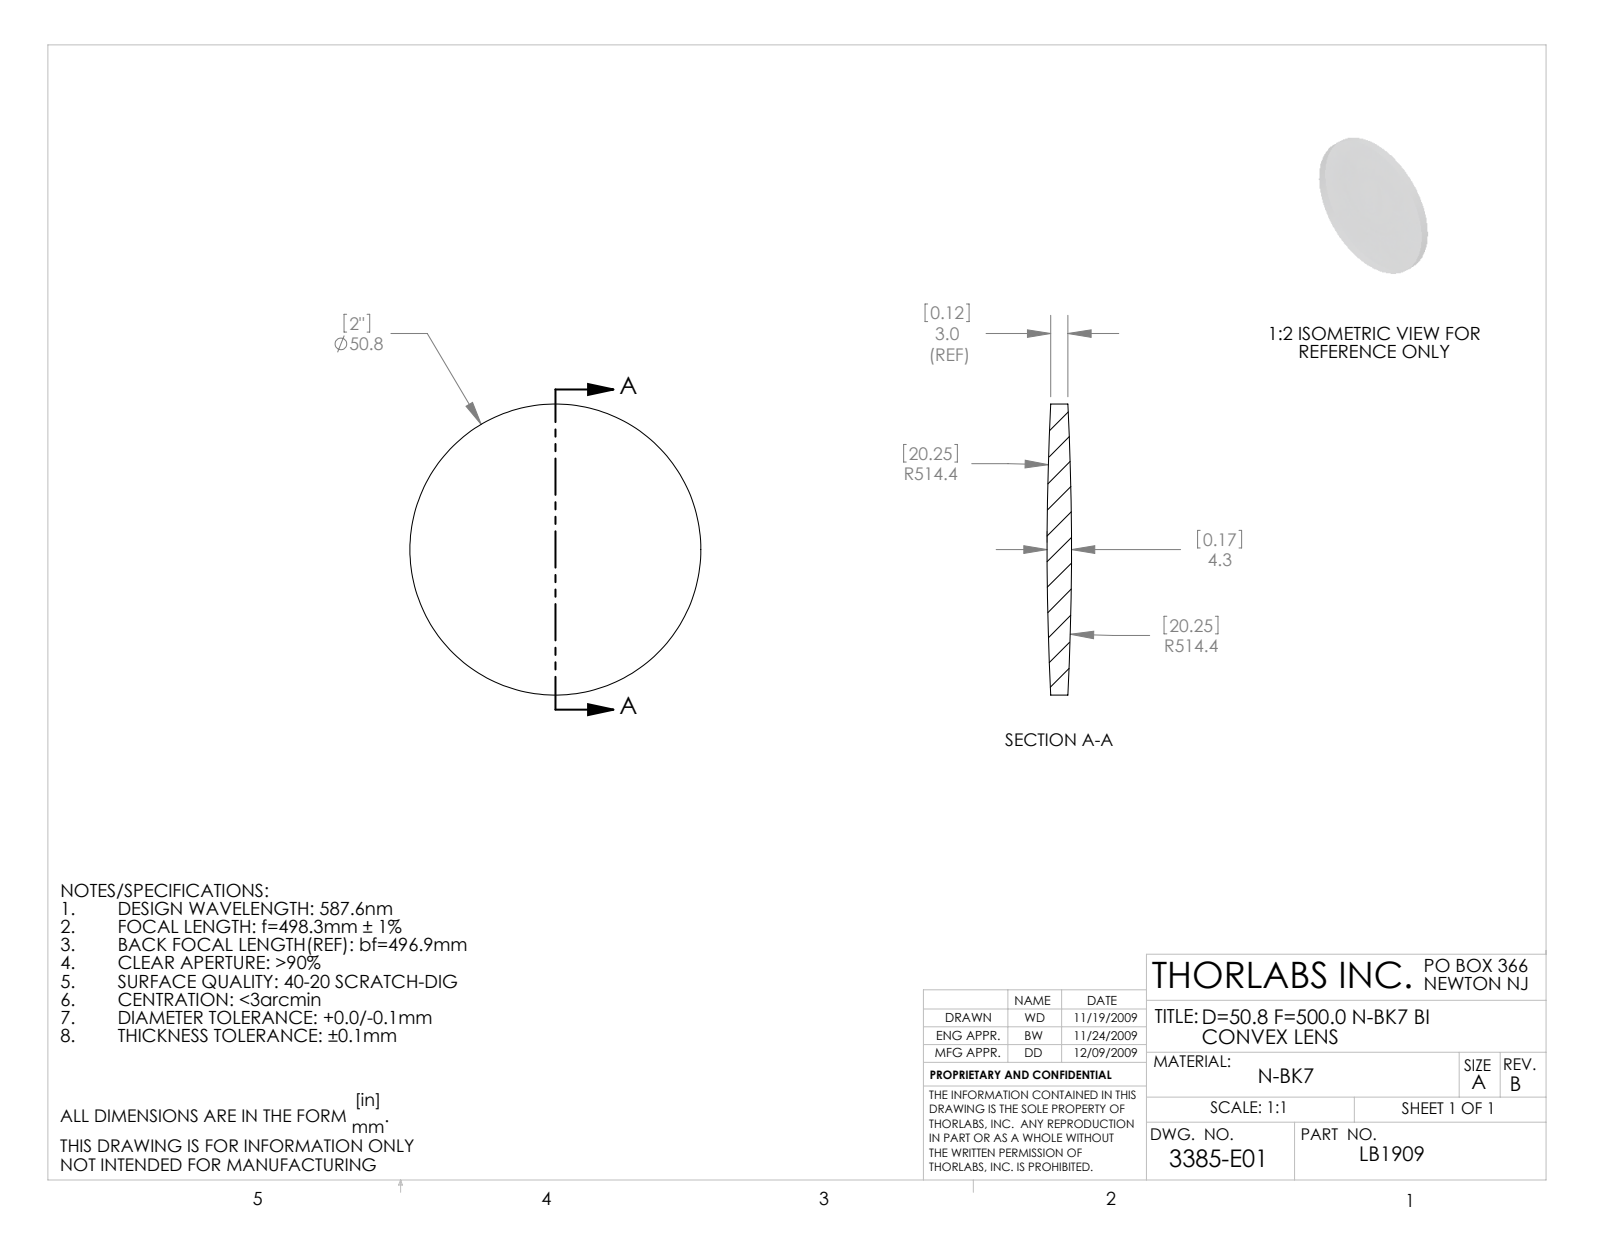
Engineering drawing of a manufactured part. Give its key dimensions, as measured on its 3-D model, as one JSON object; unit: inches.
{"part_name": "3385-E0W", "step_written_by": "SolidWorks 2009 (AUTOMOTIVE_DESIGN)", "units": "inches", "bodies": {"solids": 1, "faces": 6, "planar": 0, "cylindrical": 2, "other": 4}, "overall_size": [2, 2, 0.168], "volume_in3": 0.449, "surface_area_in2": 7.031, "round_bosses_or_shafts": [[2, 1]]}
